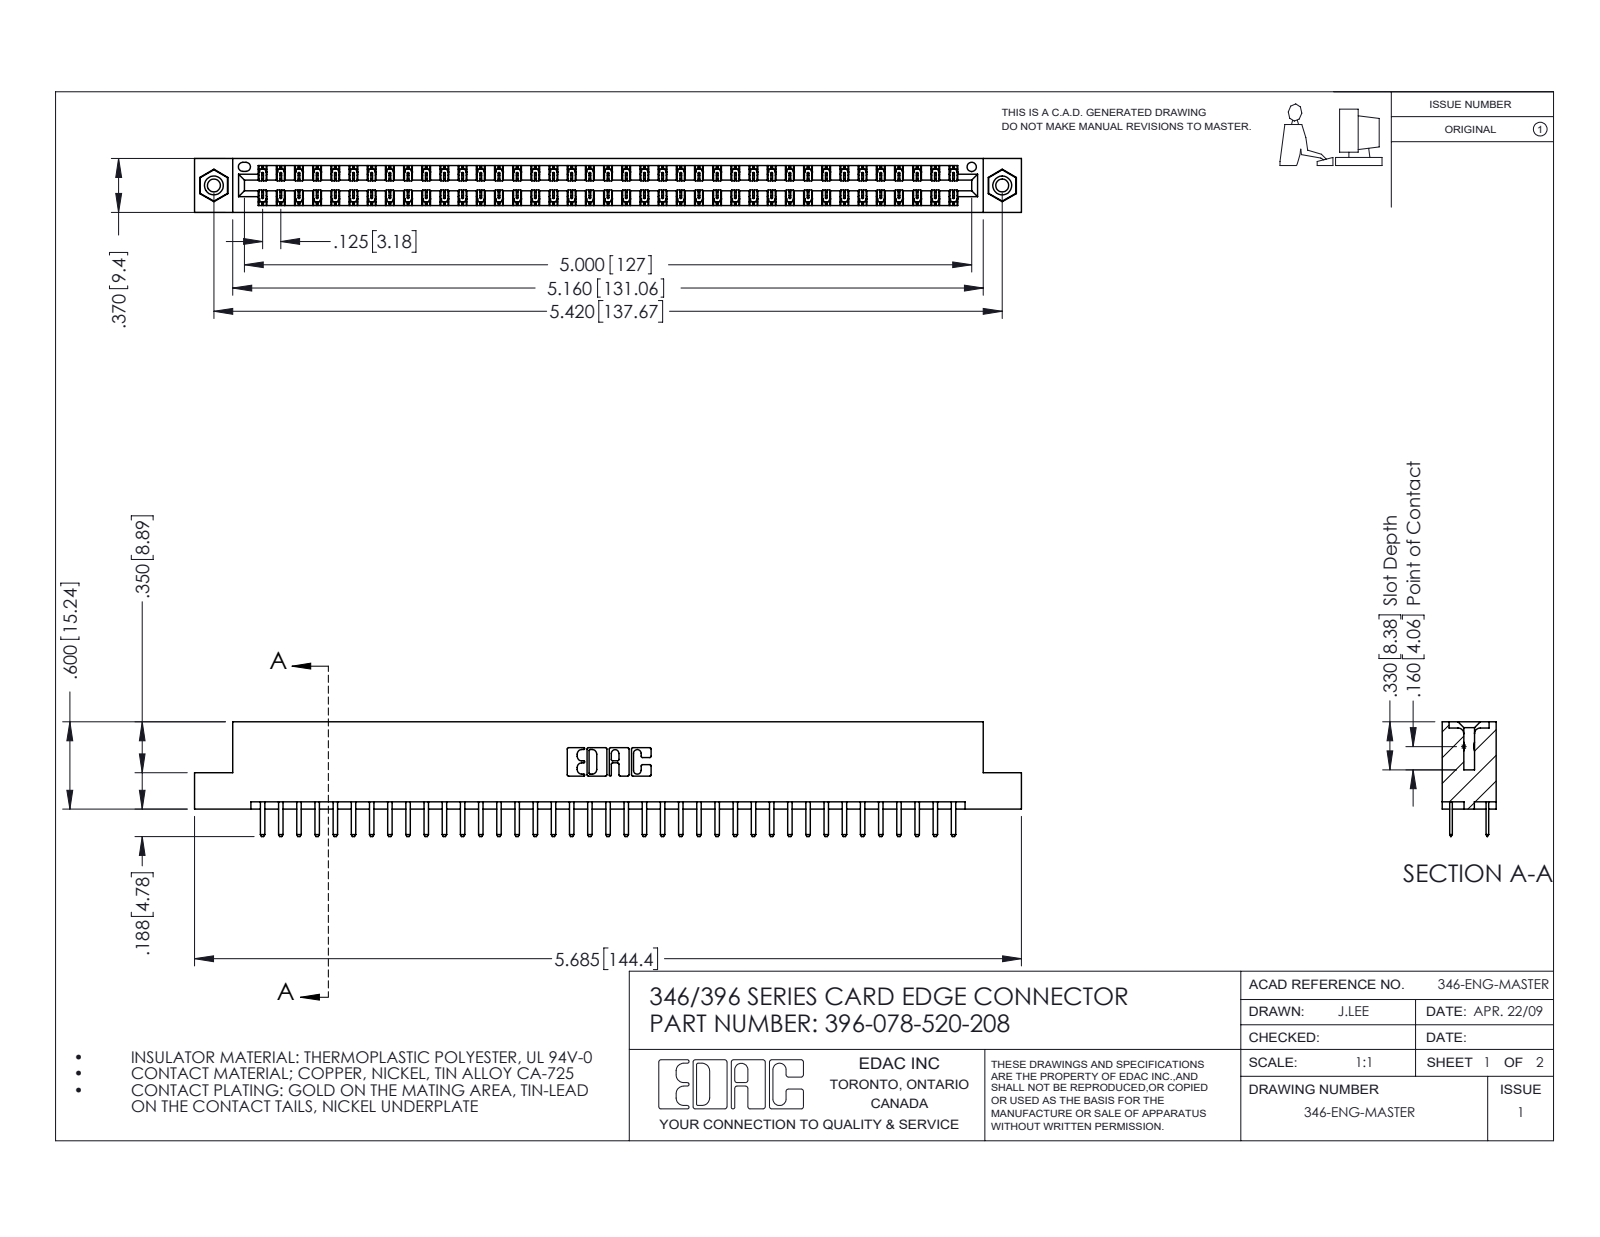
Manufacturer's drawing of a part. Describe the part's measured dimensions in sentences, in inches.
The part is named "345-292-001_345-293-120; 396-078-520-208; 346 Part_Flush Mounting Lugs - 0.156 Dia-TI; 345-250-001_345-250-003-102". Its 3-D file was written by "SolidWorks 2016 (CONFIG_CONTROL_DESIGN)". It is 81 solids with 4550 faces: 2994 planar, 1540 cylindrical and 16 other. Overall it measures 5.685 by 0.788 by 0.37 inches. Its volume is 0.855 cubic inches and its surface area 29.7 square inches. Round holes: 2 of diameter 0.089, 2 of diameter 0.125, 2 of diameter 0.156, 1 of diameter 0.064. Round bosses or shafts: 2 of diameter 0.155. Partial cylindrical surfaces (rounded edges, fillets, slot ends): 117 of radius 0.006, 82 of radius 0.01, 22 of radius 0.01, 6 of radius 0.007, 6 of radius 0.031, 3 of radius 0.026, 2 of radius 0.014, 2 of radius 0.022. The main face-to-face distances are 0.048, 0.322, 0.25, 0.37, 0.275, 0.072, 0.298, 0.025, 0.148, 0.222. The hole center spacings are 0.246, 5.211, 5.42.
